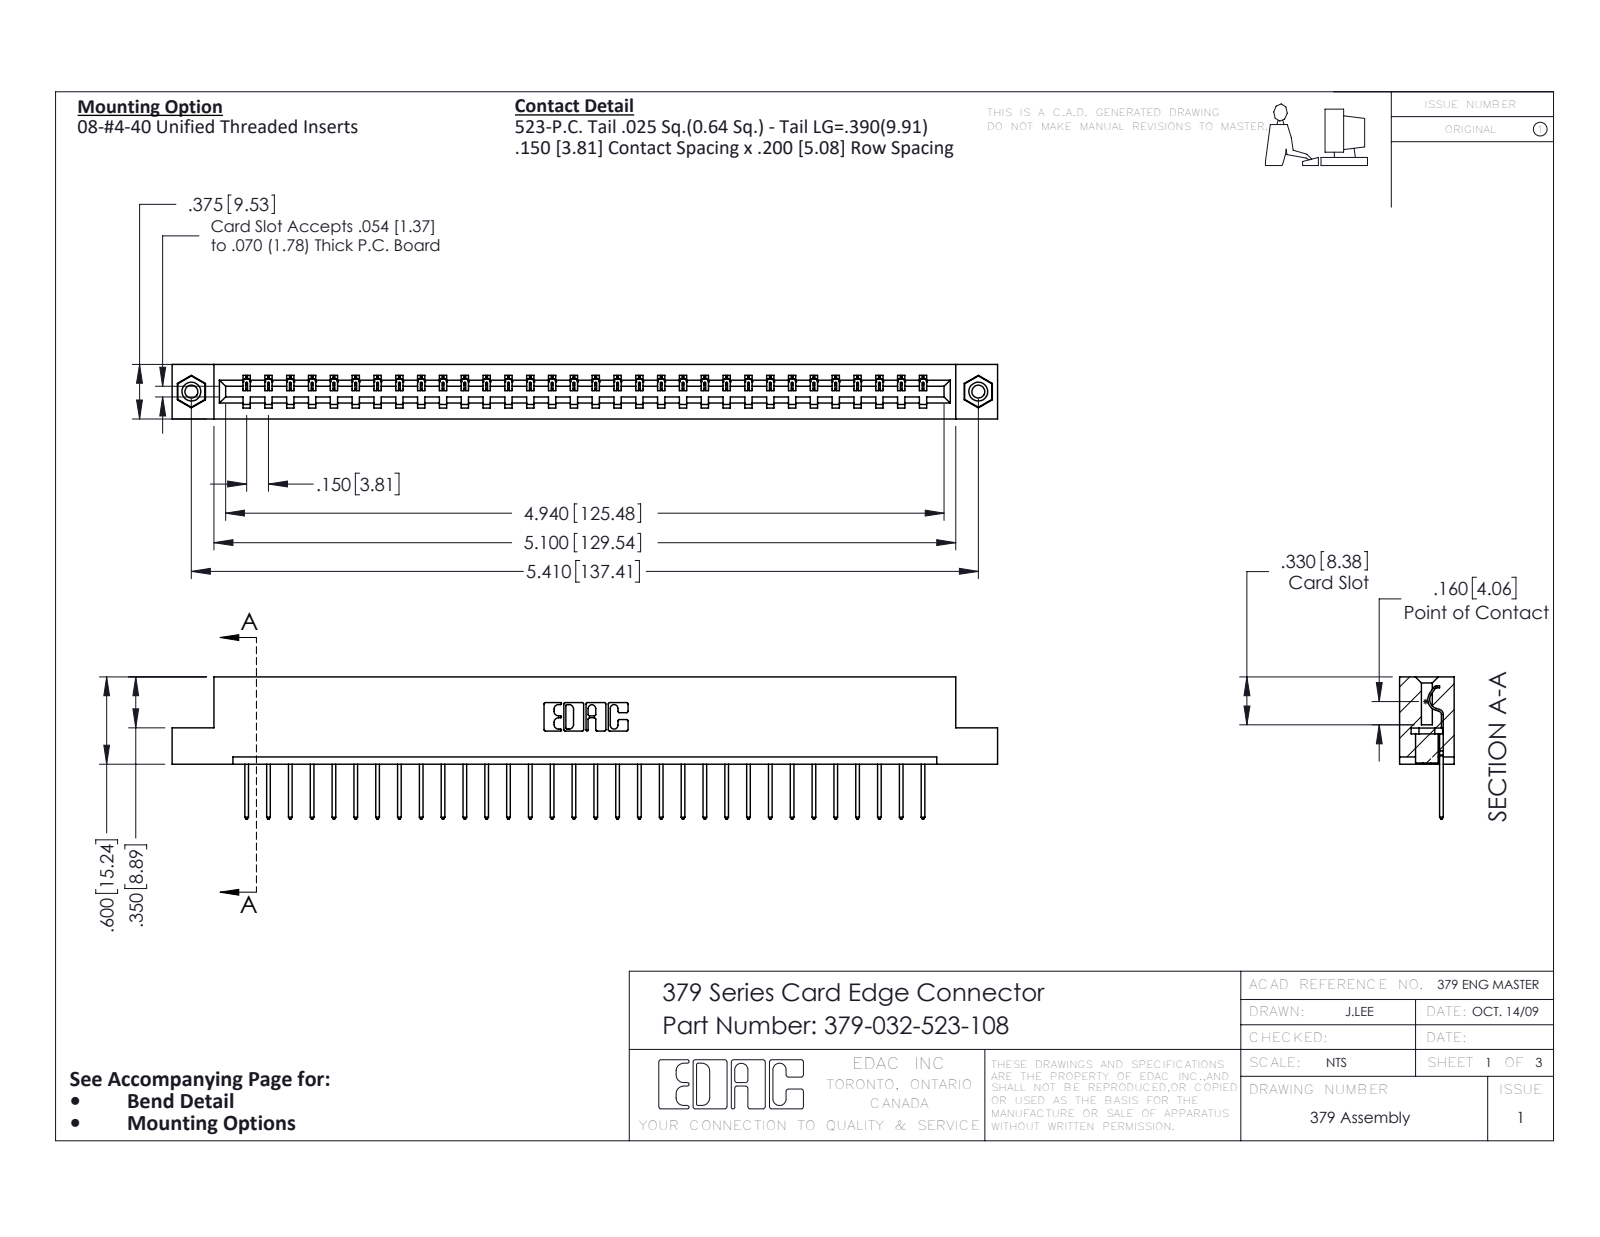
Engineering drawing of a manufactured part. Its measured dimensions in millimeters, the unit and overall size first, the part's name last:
Units: millimetres
Overall size (bounding box): 144.1 × 24.8 × 9.5
Round holes (diameter × count): ⌀2.3 ×2, ⌀3.2 ×2, ⌀4 ×2
Round bosses / shafts (diameter × count): ⌀3.9 ×2
Partial cylindrical surfaces — rounded edges, fillets, slot ends (radius × count): R0.2 ×64, R0.3 ×64, R0.3 ×22, R0.2 ×6, R0.8 ×6, R0.7 ×3, R0.4 ×1, R0.6 ×1
Main face-to-face distances: 7.6, 1.9, 9.5, 5.7, 5.1, 15.2, 7, 2.5, 0.6, 14
Hole centre spacings: 137.4
Volume: 15 000 mm³ · Surface area: 15 360 mm²
Bodies: 35 solids, 2030 faces (1446 planar, 568 cylindrical, 16 other)
Part name (STEP PRODUCT): 345-292-001_345-293-123; 345-250-001_345-250-003-102; 379 Part_Flush - .156 Dia - TI; 379-032-523-108
STEP written by: SolidWorks 2016 (CONFIG_CONTROL_DESIGN)
